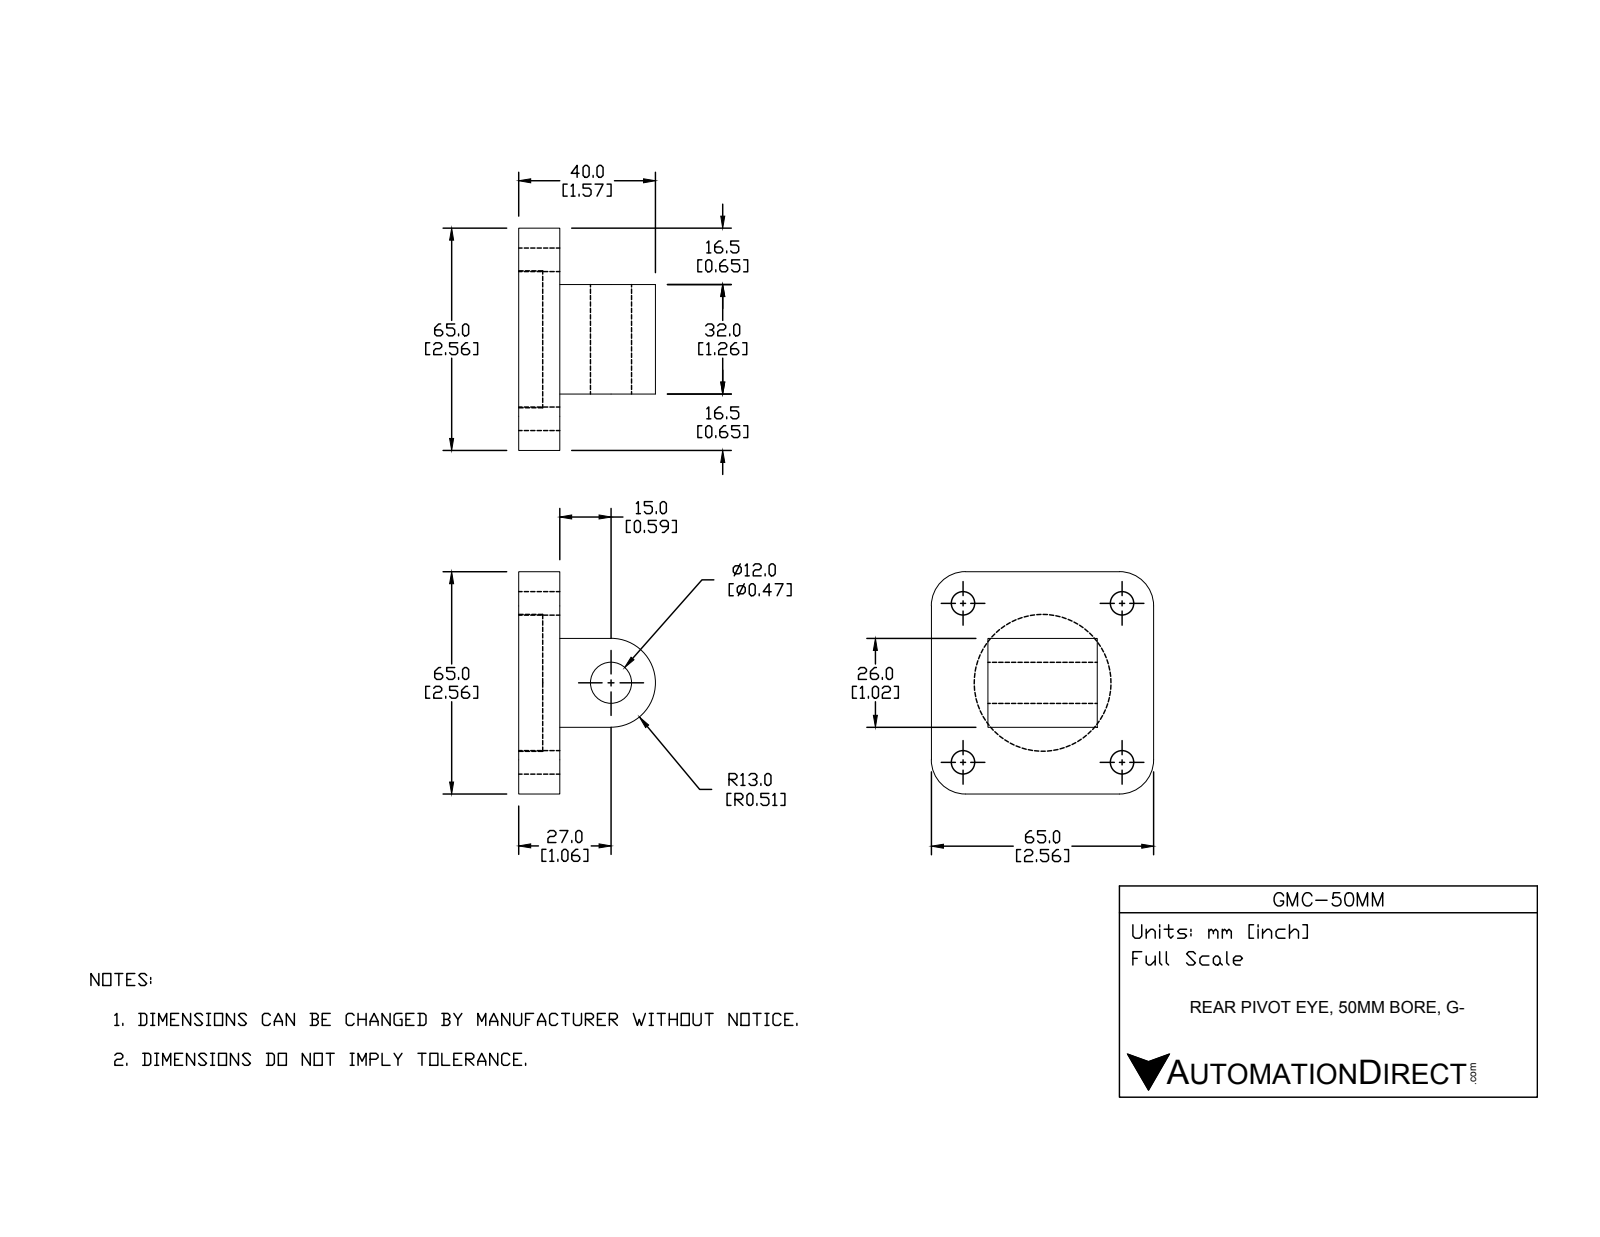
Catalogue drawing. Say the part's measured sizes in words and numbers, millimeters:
The part is named "GMC-50MM". Its 3-D file was written by "SolidWorks 2017 (AUTOMOTIVE_DESIGN)". It is 1 solid with 28 faces: 11 planar, 17 cylindrical and 0 other. Overall it measures 65 by 65 by 40 millimeters. Its volume is 56 434 cubic millimeters and its surface area 16 539 square millimeters. Round holes: 4 of diameter 6.9, 1 of diameter 12, 1 of diameter 40. Partial cylindrical surfaces (rounded edges, fillets, slot ends): 4 of radius 10, 1 of radius 13. The main face-to-face distances are 12, 7, 5, 65, 16.5, 48.5, 19.5, 45.5, 32, 26. The hole center spacings are 32.88, 46.5, 65.76.
